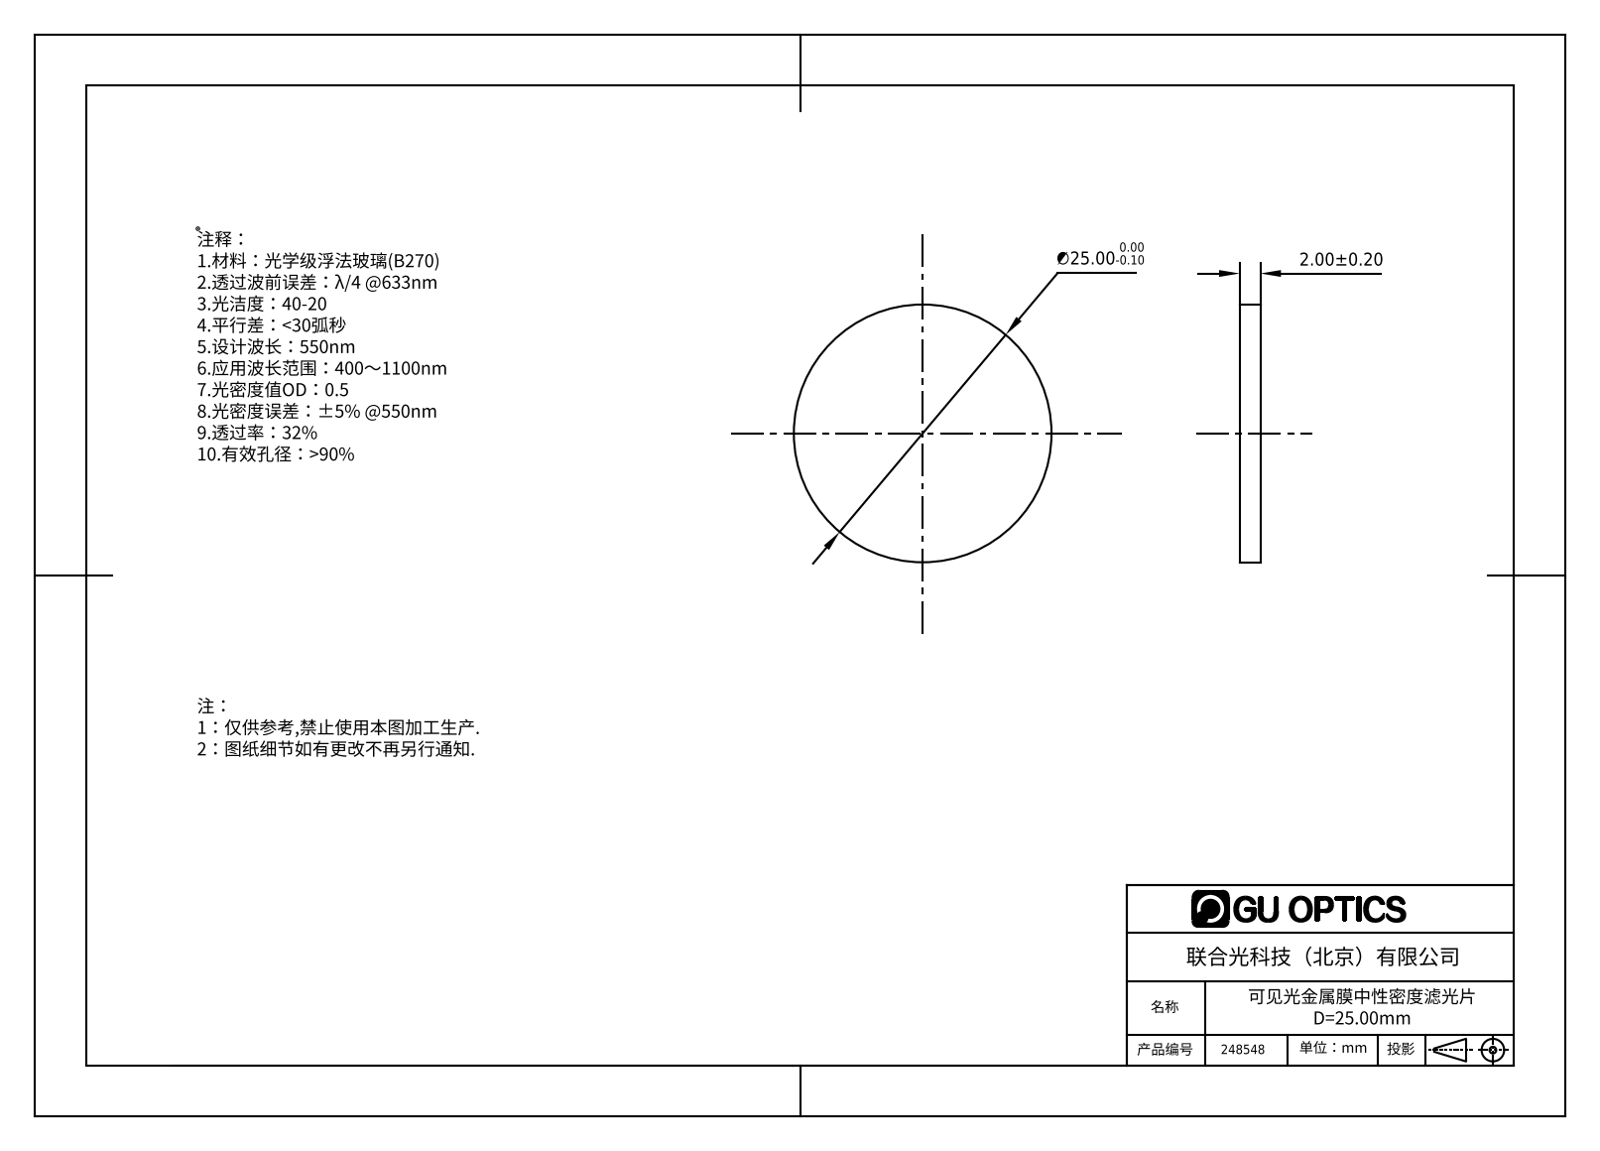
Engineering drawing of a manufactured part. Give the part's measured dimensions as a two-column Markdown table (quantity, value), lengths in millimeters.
| quantity | value |
| --- | --- |
| part name | 248511 |
| STEP written by | SolidWorks 2016 (AUTOMOTIVE_DESIGN) |
| units | millimeters |
| bodies | 1 solid, 4 faces (2 planar, 2 cylindrical, 0 other) |
| overall size | 25 × 25 × 2 |
| volume | 982 mm³ |
| surface area | 1 139 mm² |
| round bosses / shafts (diameter × count) | 25 × 1 |
| main face-to-face distances | 2 |
